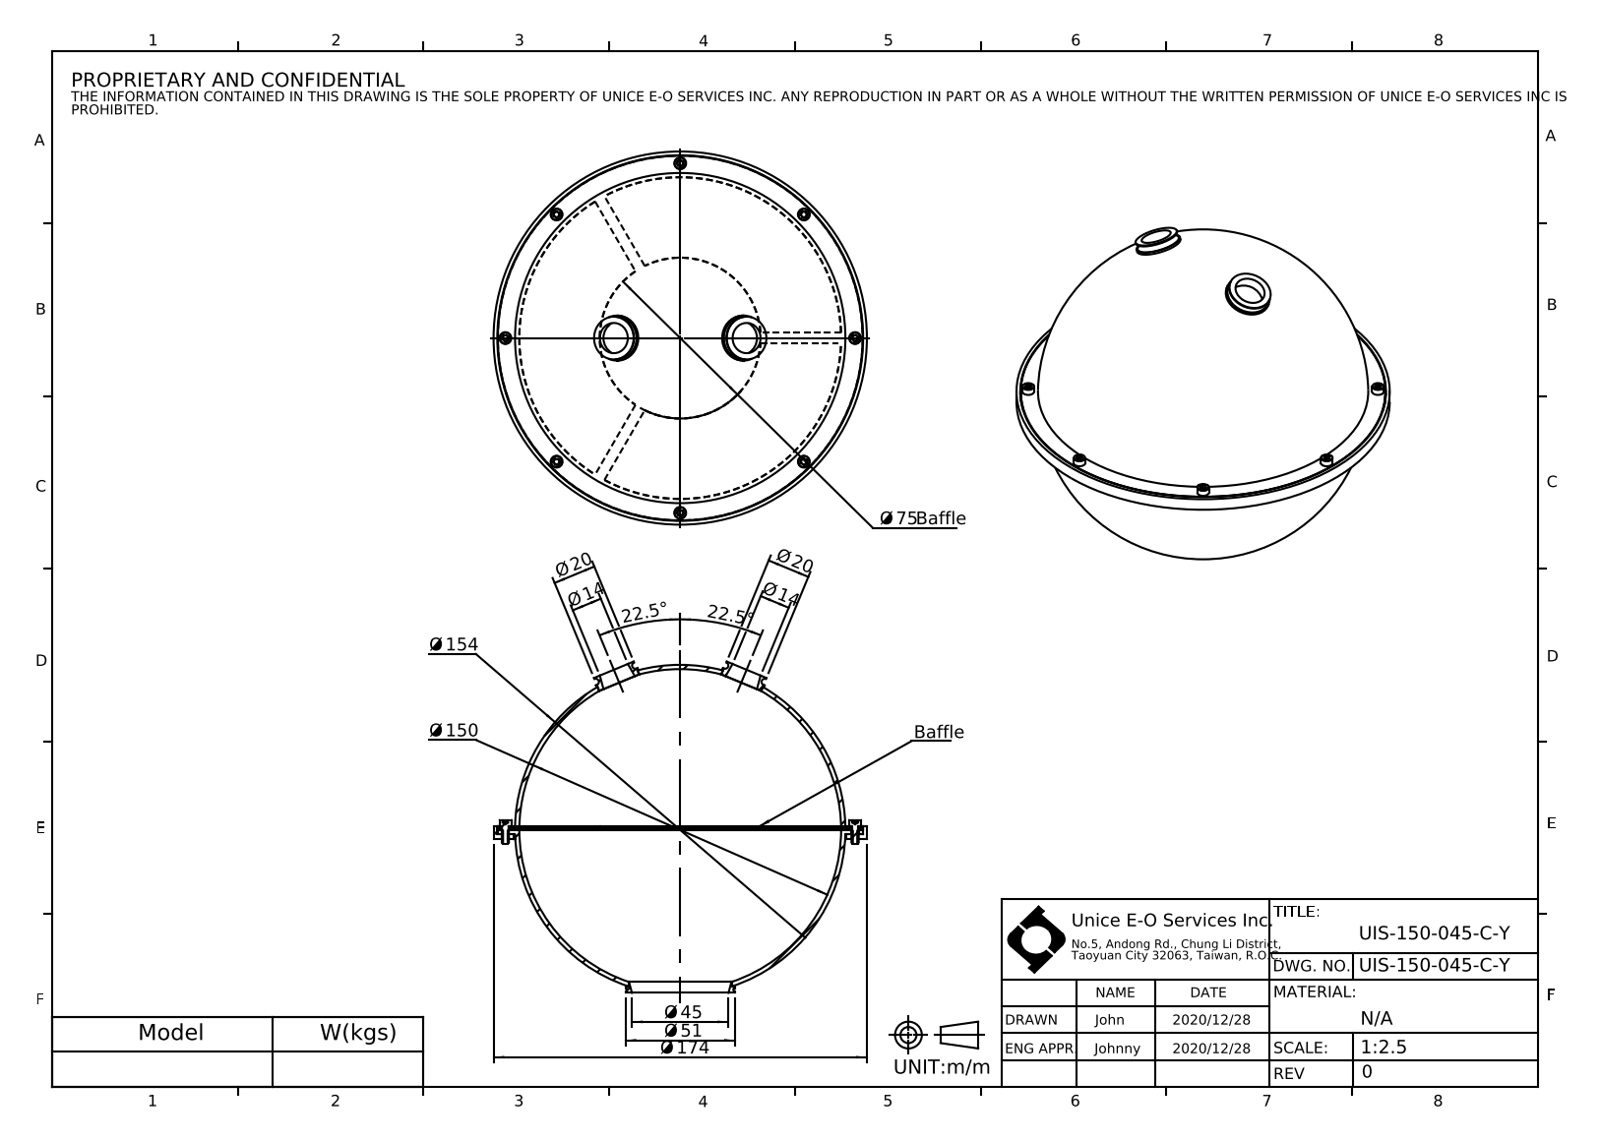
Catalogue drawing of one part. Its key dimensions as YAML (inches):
part_name: "UIS-150-045-C-Y"
step_written_by: "SolidWorks 2020 (CONFIG_CONTROL_DESIGN)"
units: inches
bodies: {solids: 0, faces: 223, planar: 71, cylindrical: 62, other: 90}
overall_size: [6.85, 6.85, 6.082]
round_holes:
  - {diameter: 6.102, count: 1}
  - {diameter: 6.713, count: 1}
round_bosses_or_shafts:
  - {diameter: 0.217, count: 8}
  - {diameter: 0.118, count: 8}
  - {diameter: 0.827, count: 2}
  - {diameter: 0.787, count: 2}
  - {diameter: 6.85, count: 1}
  - {diameter: 6.693, count: 1}
  - {diameter: 2.008, count: 1}
face_to_face_distances: [0.177, 0.059, 0.236, 0.138, 0.079, 0.098, 2.822, 2.92, 2.999, 3.058]
